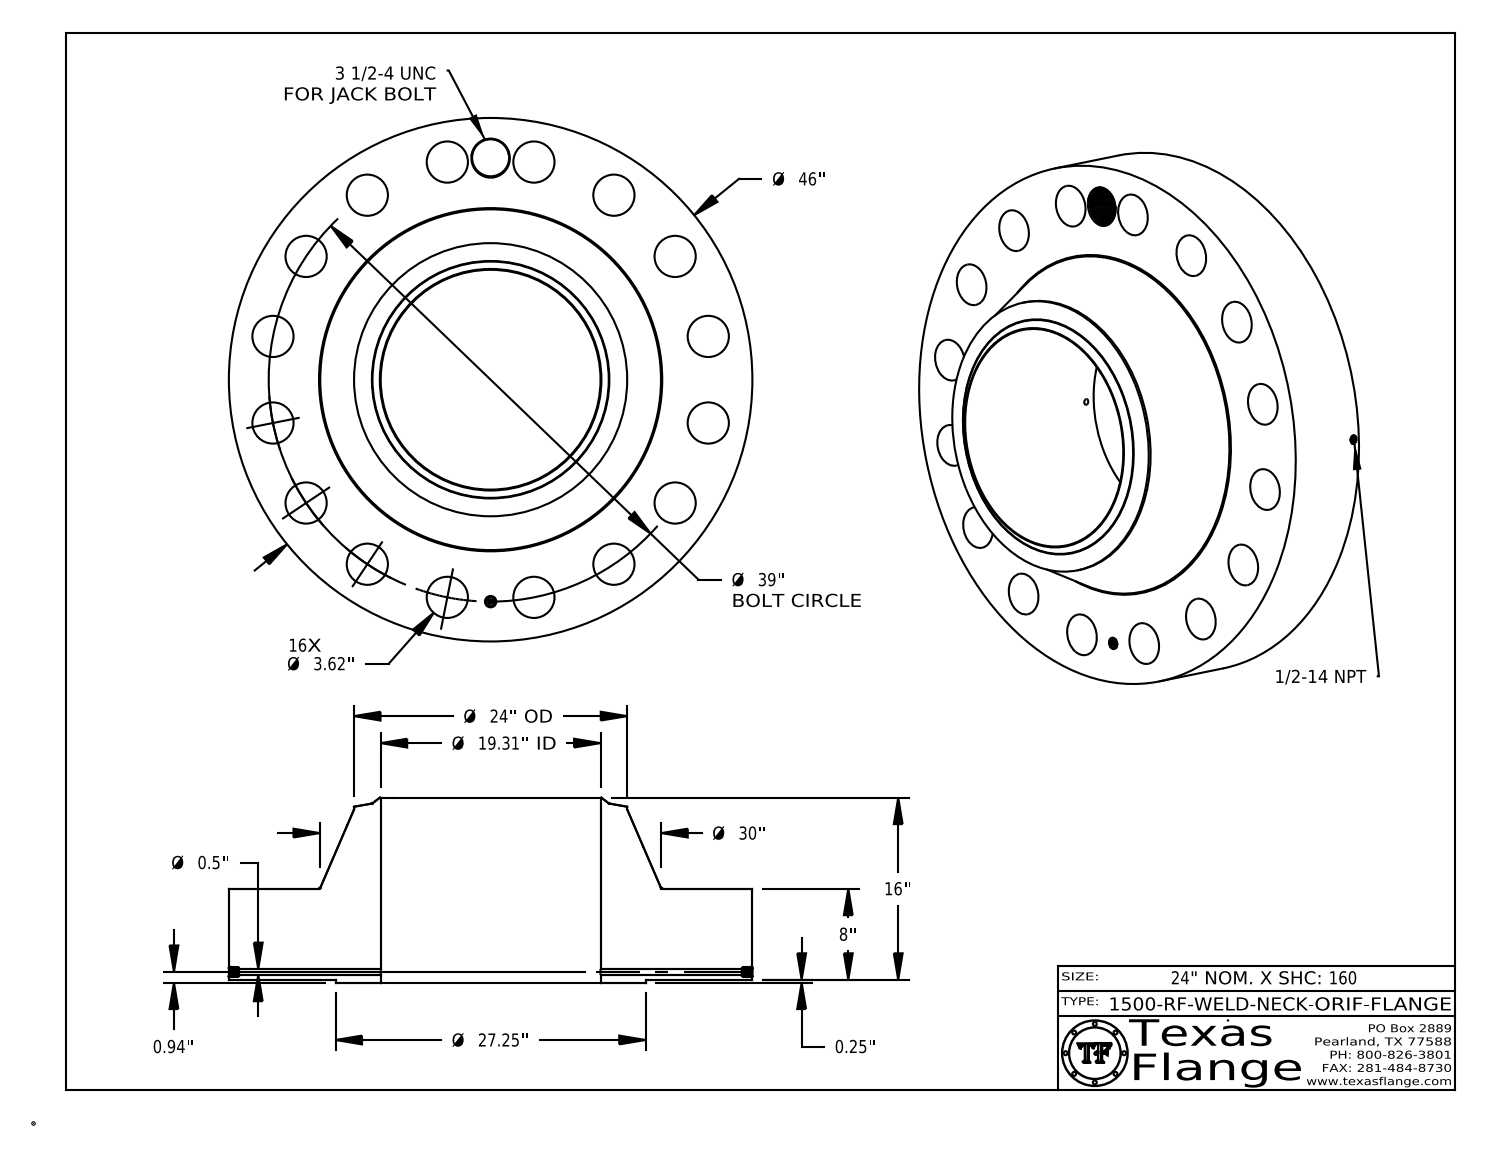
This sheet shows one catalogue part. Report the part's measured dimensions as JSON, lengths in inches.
{"part_name": "1500-RF-WELD-NECK", "step_written_by": "CATIA V5 STEP AP214 (AUTOMOTIVE_DESIGN)", "units": "inches", "bodies": {"solids": 1, "faces": 891, "planar": 369, "cylindrical": 144, "other": 378}, "overall_size": [46, 46, 16.25], "volume_in3": 11675, "surface_area_in2": 6593, "round_holes": [[3.62, 16], [0.5, 1], [0.672, 1], [1, 1], [3.25, 1], [19.312, 1]], "round_bosses_or_shafts": [[0.061, 8], [46, 1], [27.25, 1], [24, 1], [0.788, 1]], "face_to_face_distances": [8, 0.25, 8.25, 16.25, 16, 8.235, 7.985, 0.015, 8.015, 0.298], "hole_center_spacings": [19.5, 27.577, 36.031, 32.427, 7.608, 14.924, 14.925, 21.667]}
